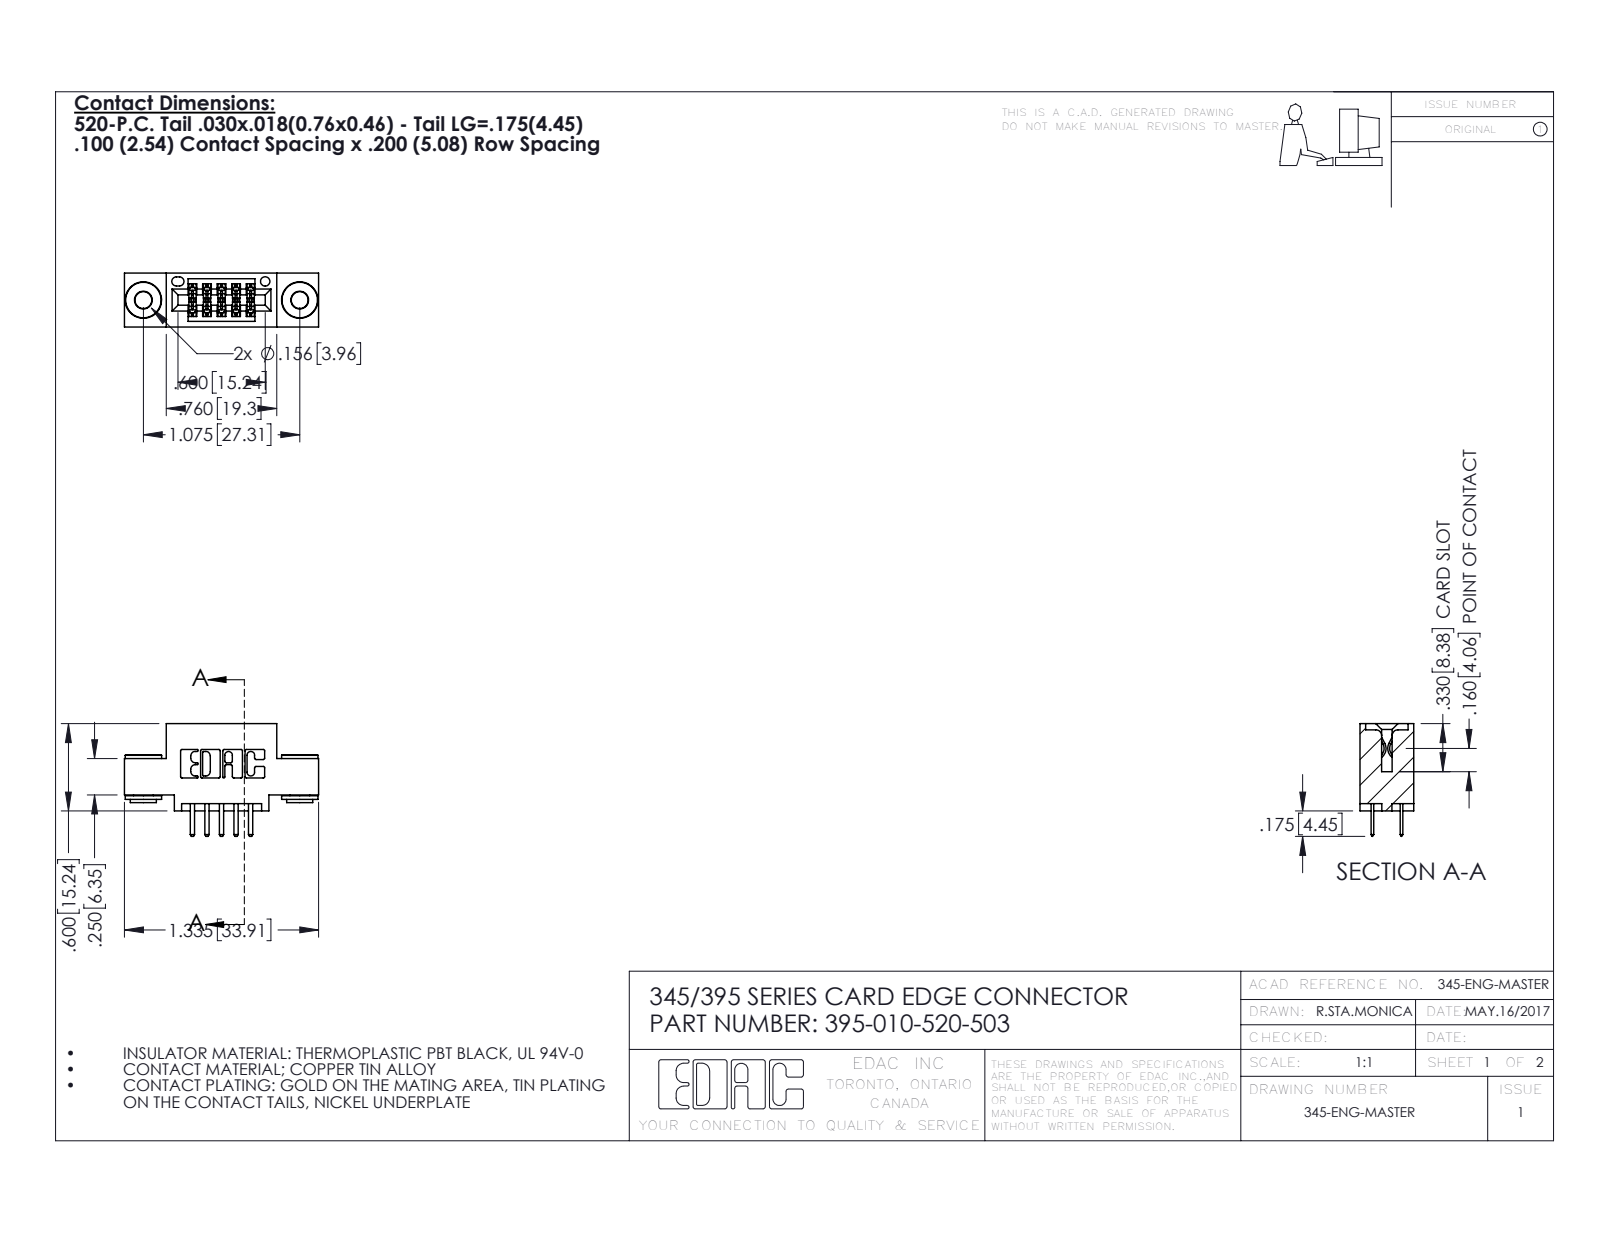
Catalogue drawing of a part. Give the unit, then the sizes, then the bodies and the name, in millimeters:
Units: millimetres
Overall size (bounding box): 33.9 × 19.7 × 9.4
Round holes (diameter × count): ⌀2.9 ×2, ⌀4 ×2, ⌀1.6 ×1
Round bosses / shafts (diameter × count): ⌀6.4 ×2, ⌀4.6 ×2, ⌀3.5 ×2
Partial cylindrical surfaces — rounded edges, fillets, slot ends (radius × count): R0.3 ×22, R0.2 ×15, R0.3 ×14, R0.2 ×6, R0.8 ×6, R0.7 ×3, R0.4 ×2, R0.5 ×2
Main face-to-face distances: 5.1, 9.4, 1.8, 7.6, 2.5, 0.6, 6.4, 1.4, 2.5, 6.9
Hole centre spacings: 6.9, 21.5, 27.3
Volume: 2 880 mm³ · Surface area: 3 847 mm²
Bodies: 13 solids, 708 faces (444 planar, 256 cylindrical, 8 other)
Part name (STEP PRODUCT): 345 Part_0.110 Offset - 0.156 Dia-TH; 345-250-002_345-250-002-102; 395-010-520-503; 345-292-001_345-293-120
STEP written by: SolidWorks 2016 (CONFIG_CONTROL_DESIGN)
